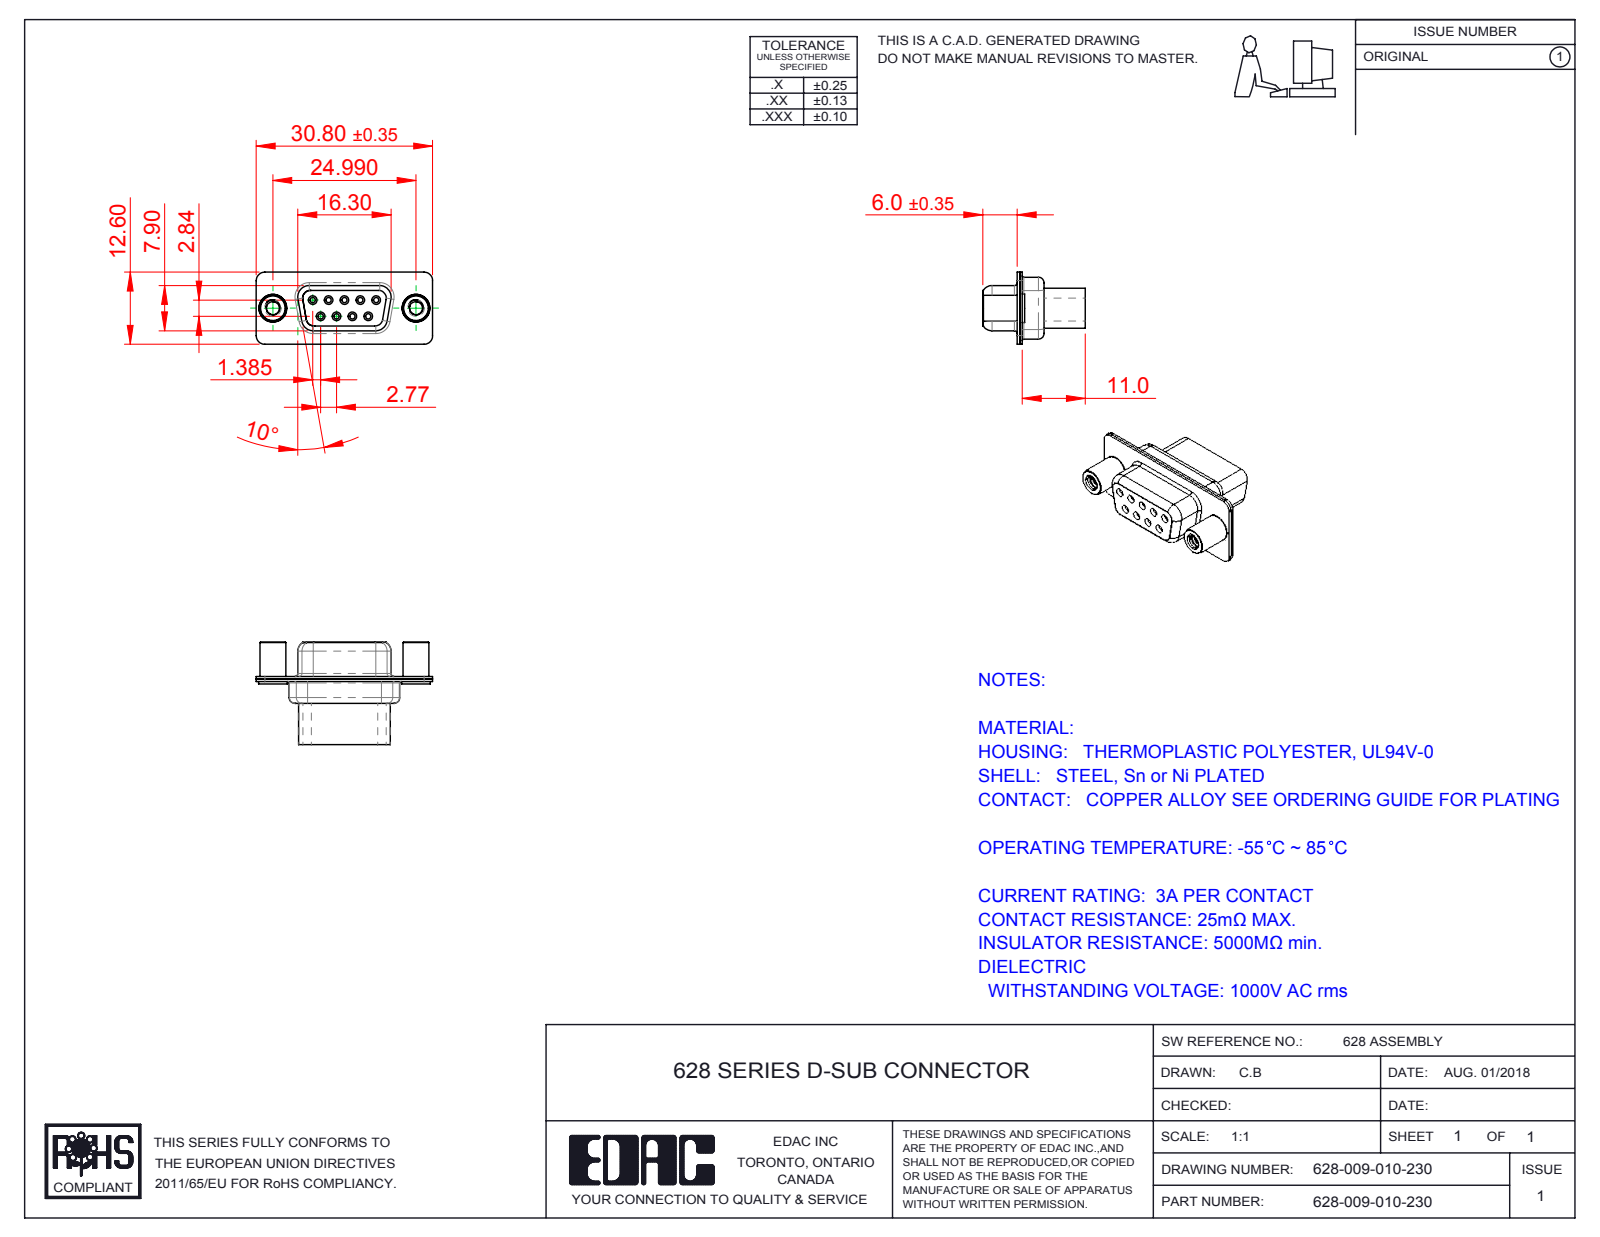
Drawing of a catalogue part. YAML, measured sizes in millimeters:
part_name: "628 Shell Rear_09 Contacts; 628 Shell Front_09 Contacts; 628 Housing_09 HP; 628 4-40 Threaded Standoff (+1 more)"
step_written_by: "SolidWorks 2016 (CONFIG_CONTROL_DESIGN)"
units: millimeters
bodies: {solids: 5, faces: 430, planar: 96, cylindrical: 237, other: 97}
overall_size: [30.8, 17.9, 12.6]
volume: 2211
surface_area: 4295
round_holes:
  - {diameter: 0.9, count: 9}
  - {diameter: 1.5, count: 9}
  - {diameter: 2, count: 9}
  - {diameter: 1.7, count: 5}
  - {diameter: 1.6, count: 4}
  - {diameter: 2.26, count: 2}
  - {diameter: 4, count: 2}
  - {diameter: 4.05, count: 2}
  - {diameter: 4.85, count: 2}
round_bosses_or_shafts:
  - {diameter: 5, count: 2}
  - {diameter: 4.95, count: 2}
  - {diameter: 4.8, count: 2}
  - {diameter: 4.5, count: 2}
partial_cylinders:
  - {radius: 1.5, count: 17}
  - {radius: 2, count: 12}
  - {radius: 1.35, count: 6}
  - {radius: 0.25, count: 4}
  - {radius: 0.5, count: 4}
  - {radius: 0.6, count: 4}
  - {radius: 0.65, count: 4}
  - {radius: 0.95, count: 4}
face_to_face_distances: [0.45, 0.4, 0.9, 6.6, 1.9, 8.5, 1.4, 7, 0.85, 0.5]
hole_center_spacings: [3.16, 2.77, 5.54, 5.03, 5.04, 8.31, 7.48, 7.49]
